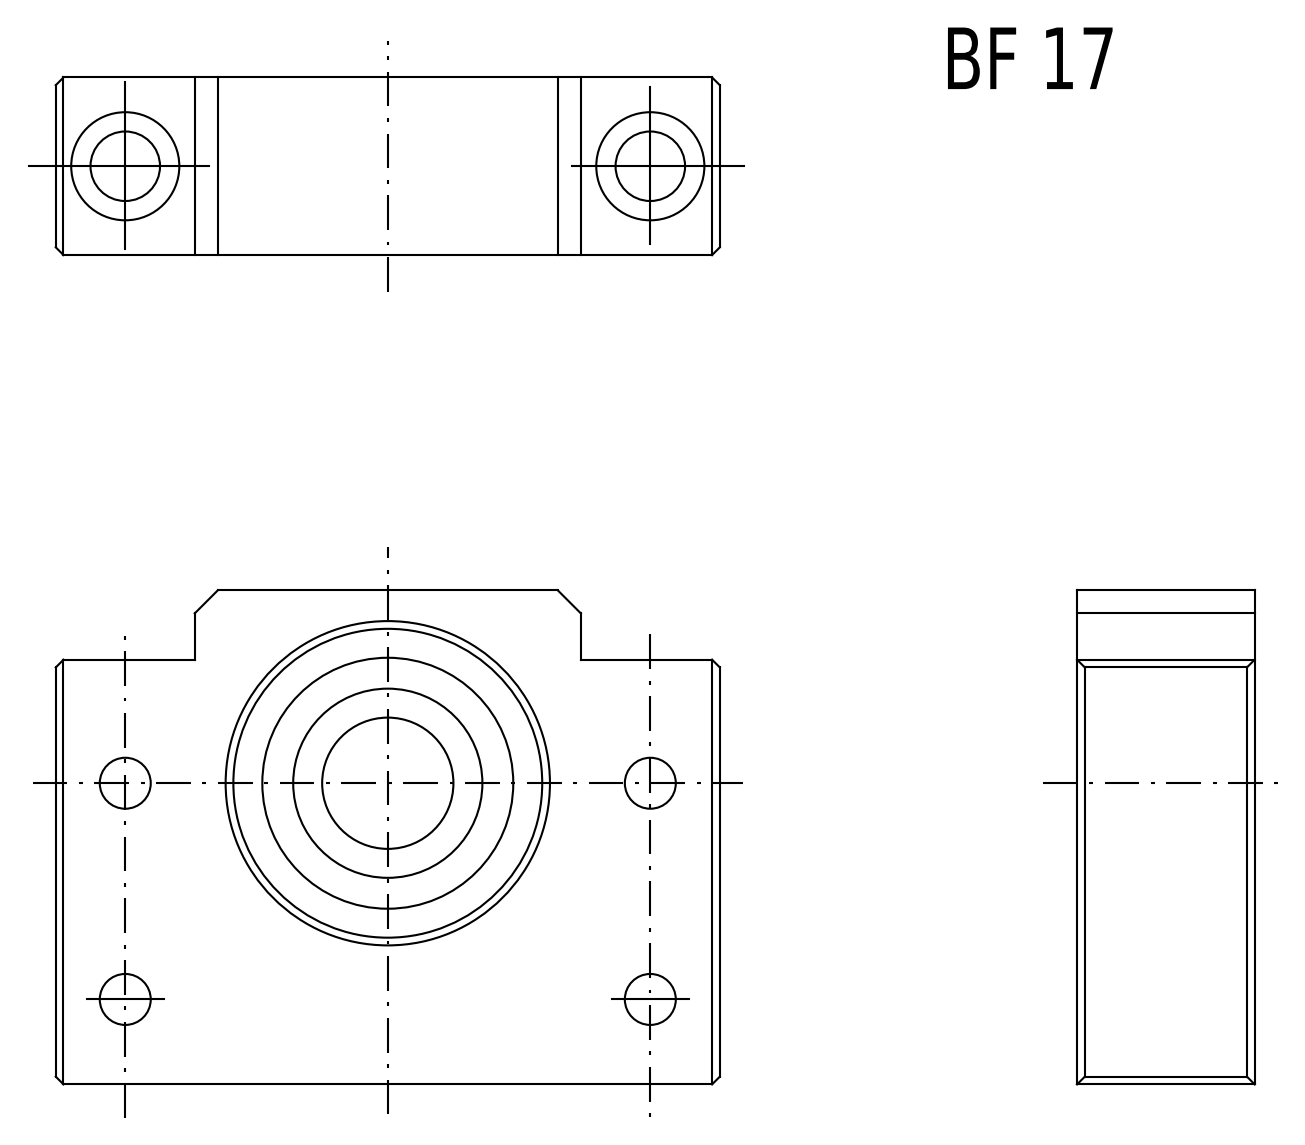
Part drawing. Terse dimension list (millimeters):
name: BF17組合件
written by: SolidWorks 2008 (CONFIG_CONTROL_DESIGN)
unit: mm
bodies: 15 solids, 158 faces (50 planar, 38 cylindrical, 70 other)
size: 86 × 64 × 23
volume: 86 916 mm³; area: 27 973 mm²
holes: 4× ⌀6.6, 2× ⌀9, 2× ⌀14, 1× ⌀17, 1× ⌀35, 1× ⌀40
bosses: 1× ⌀22
face distances: 23, 86, 64, 17.5, 5.5, 55, 9, 18, 68, 12
hole spacings: 68, 28, 34, 44.05, 73.54
